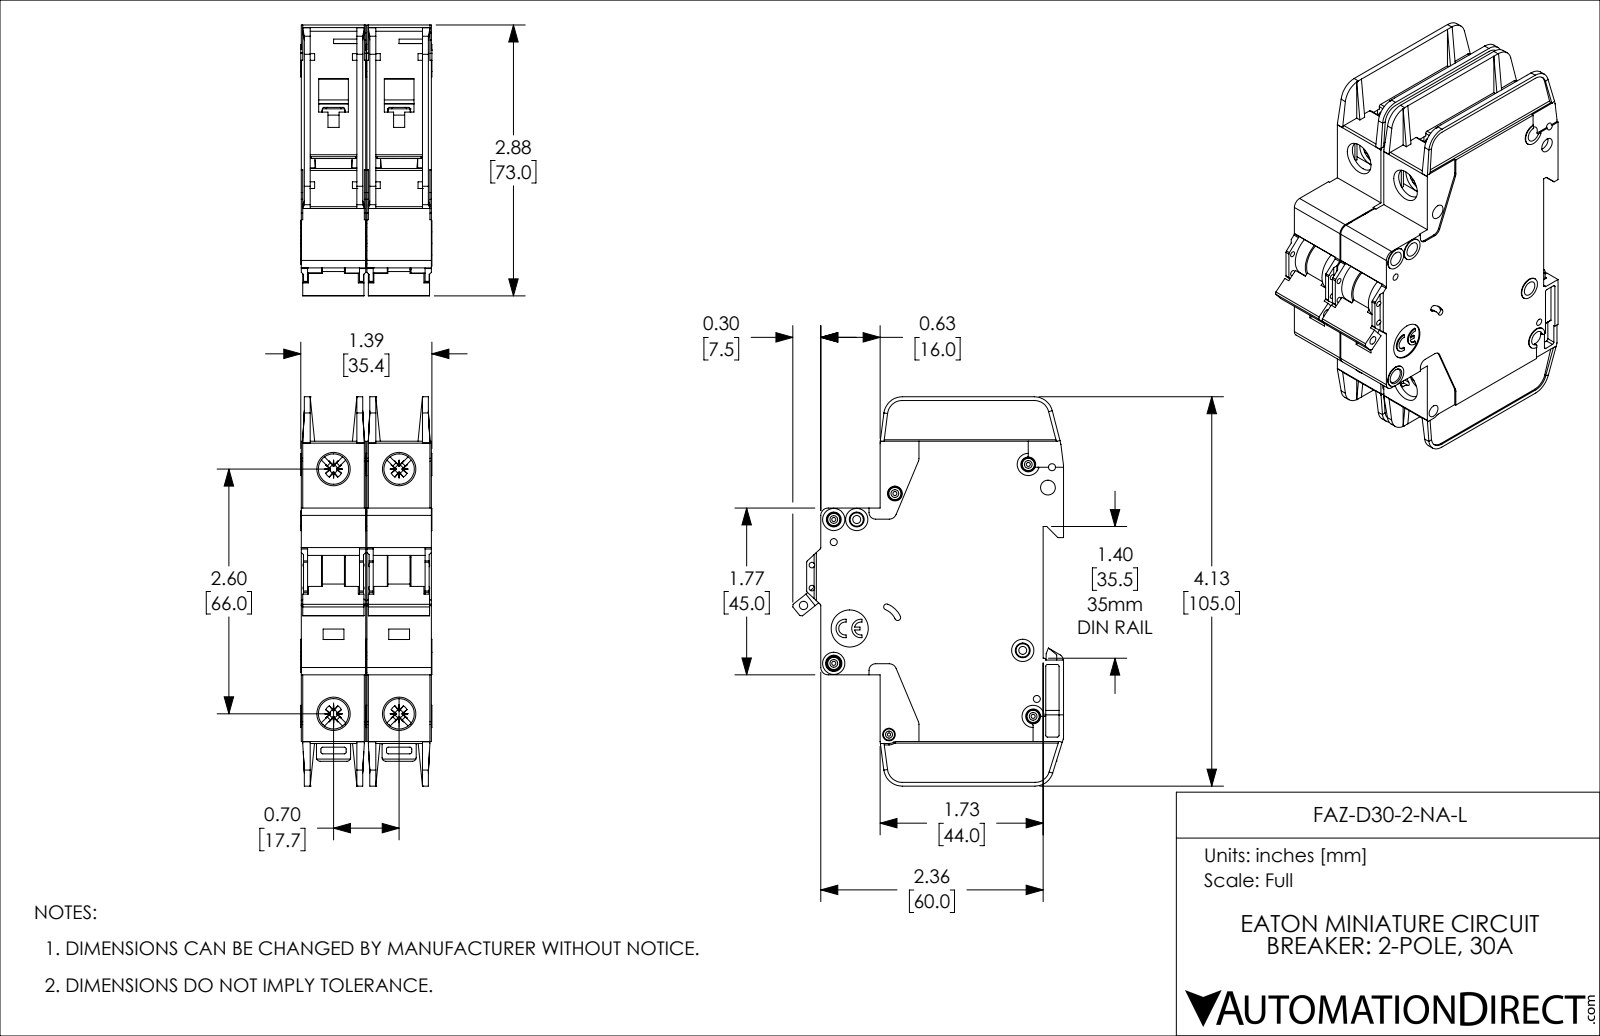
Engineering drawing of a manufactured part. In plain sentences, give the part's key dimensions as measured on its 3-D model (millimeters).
The part is named "FAZ-D30-2-NA-L". Its 3-D file was written by "SolidWorks 2019 (AUTOMOTIVE_DESIGN)". It is 2 solids with 2254 faces: 1342 planar, 714 cylindrical and 198 other. Overall it measures 105 by 73.1 by 35.4 millimeters. Its volume is 153 500 cubic millimeters and its surface area 52 910 square millimeters. Round holes: 8 of diameter 4, 5 of diameter 1.1, 4 of diameter 1.9, 4 of diameter 8.2, 2 of diameter 1.5, 2 of diameter 2.2, 1 of diameter 0.9, 1 of diameter 2.3, 1 of diameter 2.5, 1 of diameter 3.4, 1 of diameter 10. Round bosses or shafts: 5 of diameter 3.3, 4 of diameter 6, 3 of diameter 3, 2 of diameter 2.5. Partial cylindrical surfaces (rounded edges, fillets, slot ends): 57 of radius 0.5, 20 of radius 0.4, 14 of radius 1, 10 of radius 2, 8 of radius 1.1, 5 of radius 0.2, 5 of radius 5, 4 of radius 0.3. The main face-to-face distances are 17.7, 1.2, 17.4, 15, 2.4, 16.2, 13.8, 35.1, 18.9, 16.5. The hole center spacings are 6.2, 13.6, 17.7, 22.1, 66, 68.3, 4.8, 5.1.
